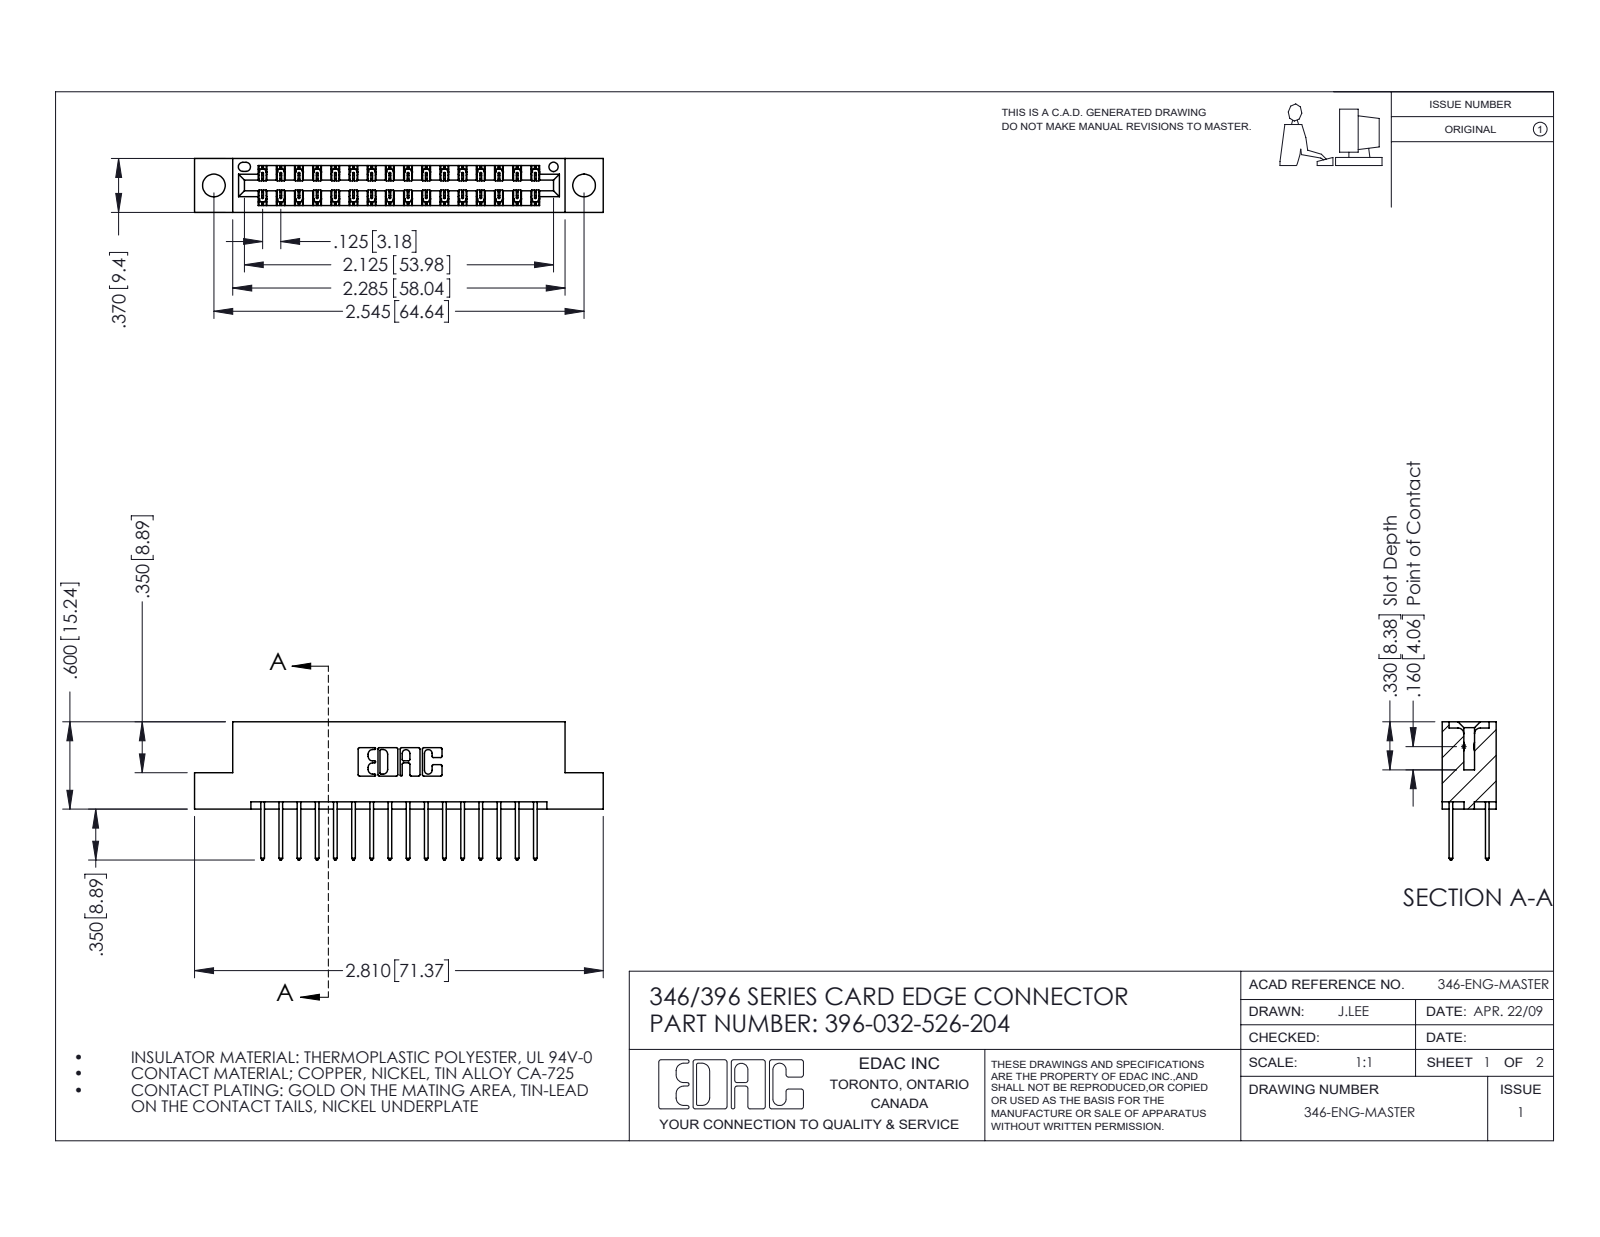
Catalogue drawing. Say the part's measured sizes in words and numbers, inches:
The part is named "346 Part_Flush Mounting Lugs - 0.156 Dia-TH; 396-032-526-204; 345-292-001_345-293-126". Its 3-D file was written by "SolidWorks 2016 (CONFIG_CONTROL_DESIGN)". It is 33 solids with 1786 faces: 1196 planar, 590 cylindrical and 0 other. Overall it measures 2.81 by 0.95 by 0.37 inches. Its volume is 0.41 cubic inches and its surface area 13.76 square inches. Round holes: 2 of diameter 0.156, 1 of diameter 0.064. Partial cylindrical surfaces (rounded edges, fillets, slot ends): 48 of radius 0.006, 32 of radius 0.01, 22 of radius 0.01, 6 of radius 0.007, 6 of radius 0.031, 3 of radius 0.026, 2 of radius 0.014, 2 of radius 0.022. The main face-to-face distances are 0.048, 0.322, 0.25, 0.37, 0.072, 0.298, 0.025, 0.275, 0.148, 0.222. The hole center spacings are 0.246, 2.338, 2.545.
